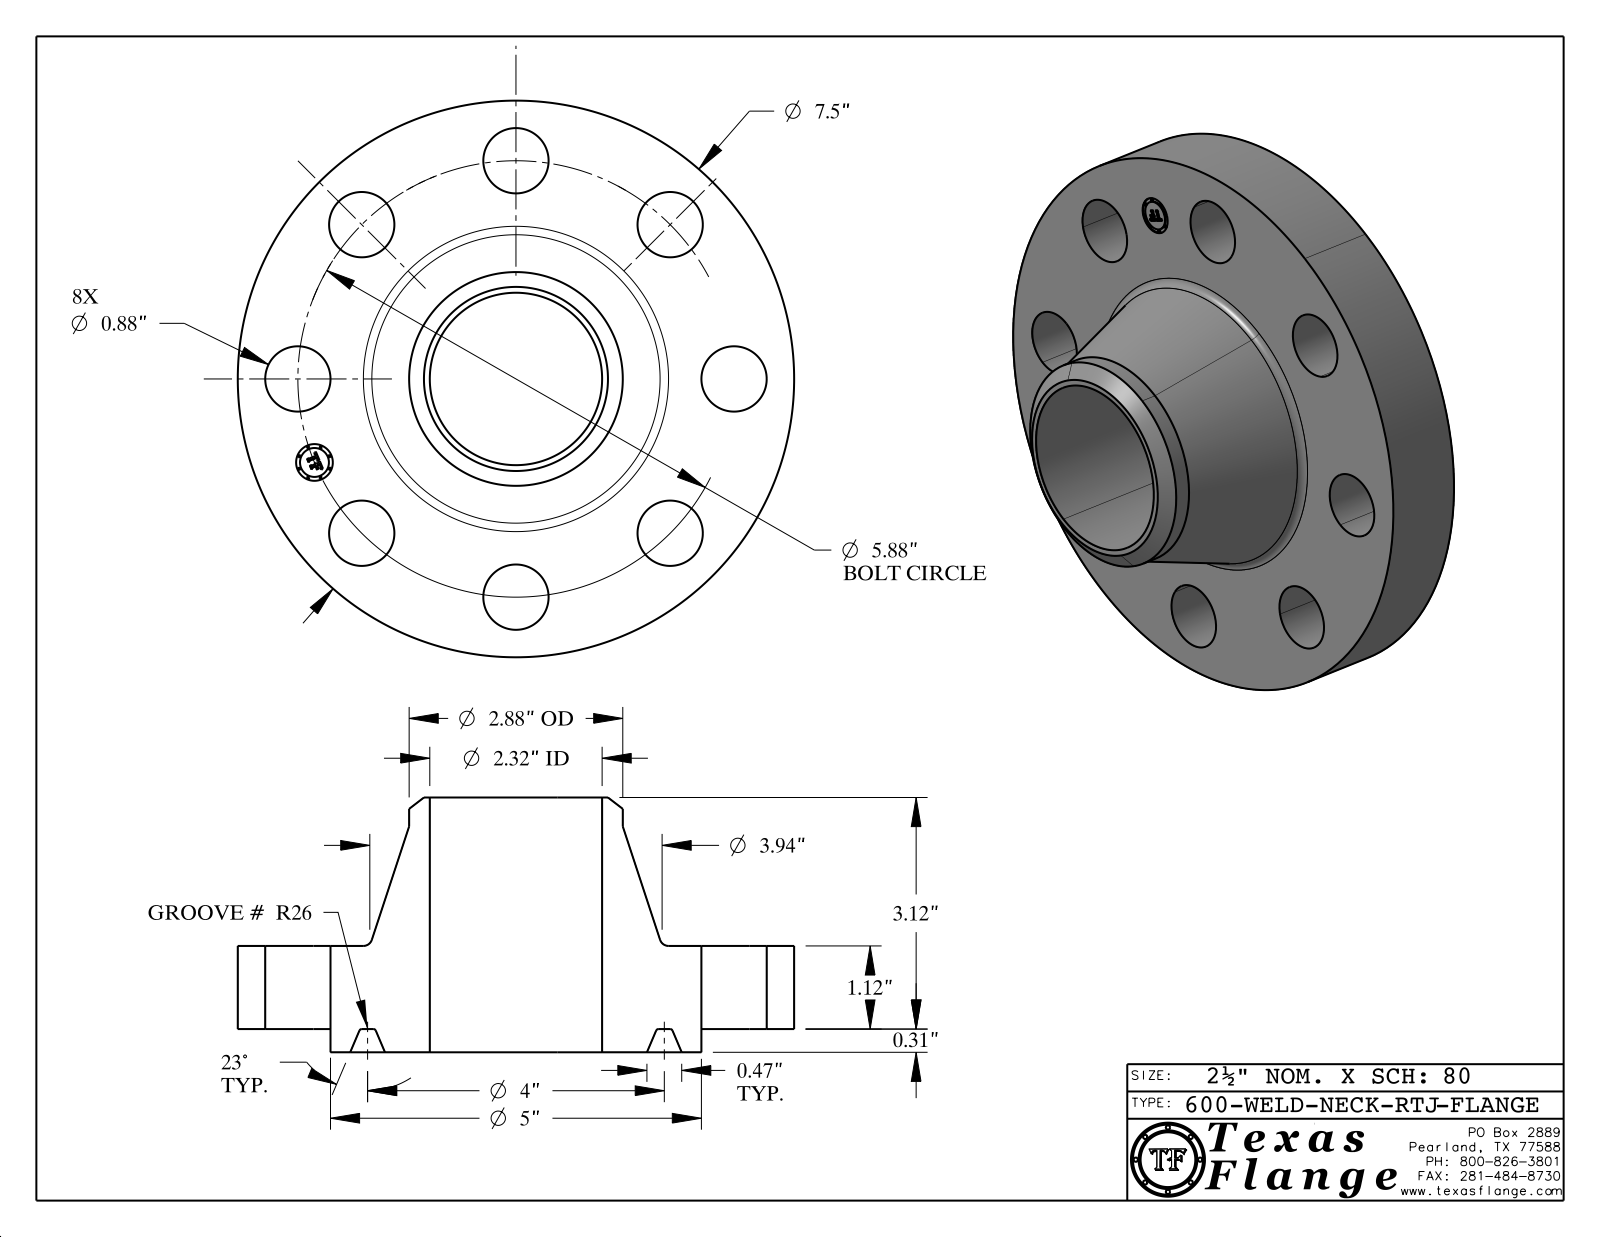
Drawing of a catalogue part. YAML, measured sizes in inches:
part_name: "600-WELD-NECK-RTJ"
step_written_by: "CATIA V5 STEP AP214 (AUTOMOTIVE_DESIGN)"
units: inches
bodies: {solids: 1, faces: 429, planar: 371, cylindrical: 44, other: 14}
overall_size: [7.5, 7.5, 3.433]
volume: 51.55
surface_area: 171.2
round_holes:
  - {diameter: 0.88, count: 8}
  - {diameter: 0.495, count: 1}
  - {diameter: 2.323, count: 1}
round_bosses_or_shafts:
  - {diameter: 0.03, count: 8}
  - {diameter: 7.5, count: 1}
  - {diameter: 5, count: 1}
  - {diameter: 2.88, count: 1}
  - {diameter: 0.39, count: 1}
face_to_face_distances: [1.12, 0.313, 1.433, 3.433, 3.12, 2, 0.015, 1.418, 1.105, 2.015]
hole_center_spacings: [2.25, 5.432, 2.94, 2.94, 4.157, 4.158, 3.267, 5.88]
